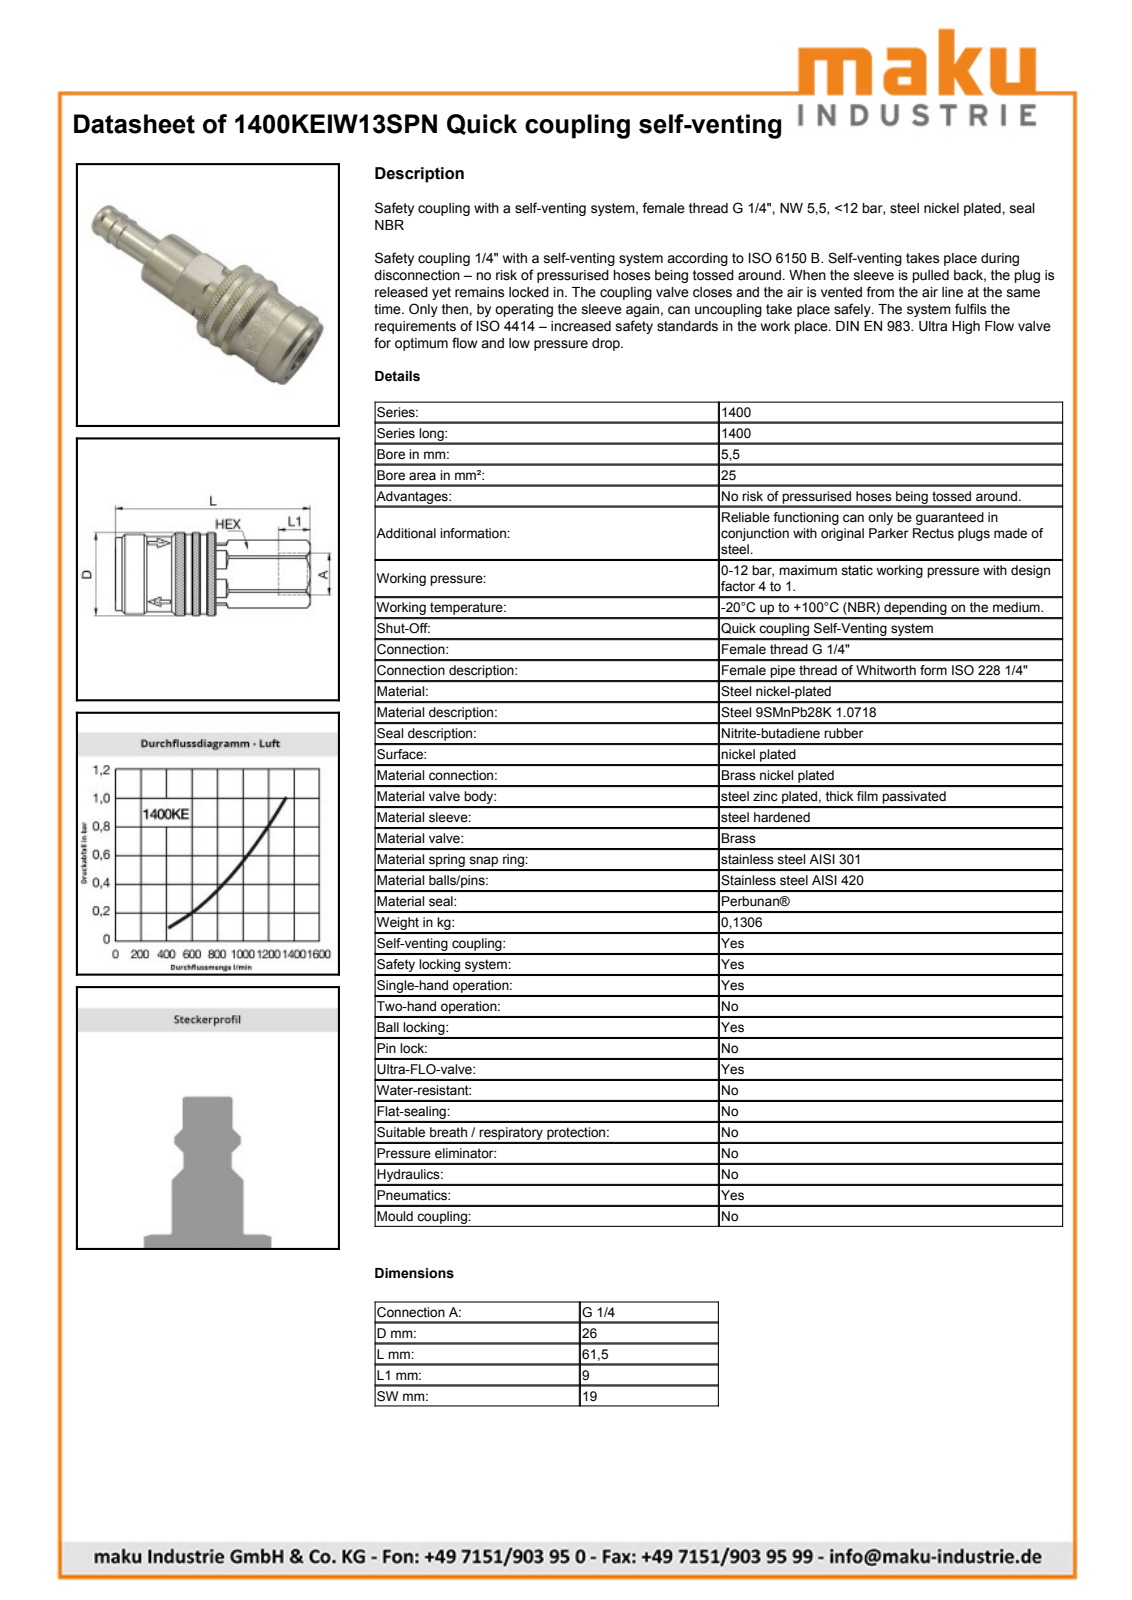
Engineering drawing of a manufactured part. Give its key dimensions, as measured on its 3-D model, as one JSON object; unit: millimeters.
{"part_name": "1400KEIW13SPN", "step_written_by": "Autodesk Inventor 2014 (AUTOMOTIVE_DESIGN)", "units": "millimeters", "bodies": {"solids": 1, "faces": 674, "planar": 297, "cylindrical": 76, "other": 301}, "overall_size": [61.5, 27, 27], "volume_mm3": 23782, "surface_area_mm2": 6041, "round_holes": [[11.8, 1]], "round_bosses_or_shafts": [[27, 1], [26, 1], [25, 1], [23.5, 1], [23, 1]], "partial_cylinders_radius": [[9.65, 1], [10.7, 1], [11.55, 1]], "face_to_face_distances": [19, 31.8, 29.7, 61.5, 61.2, 31.5, 10.01, 19.69, 51.19, 51.49]}
